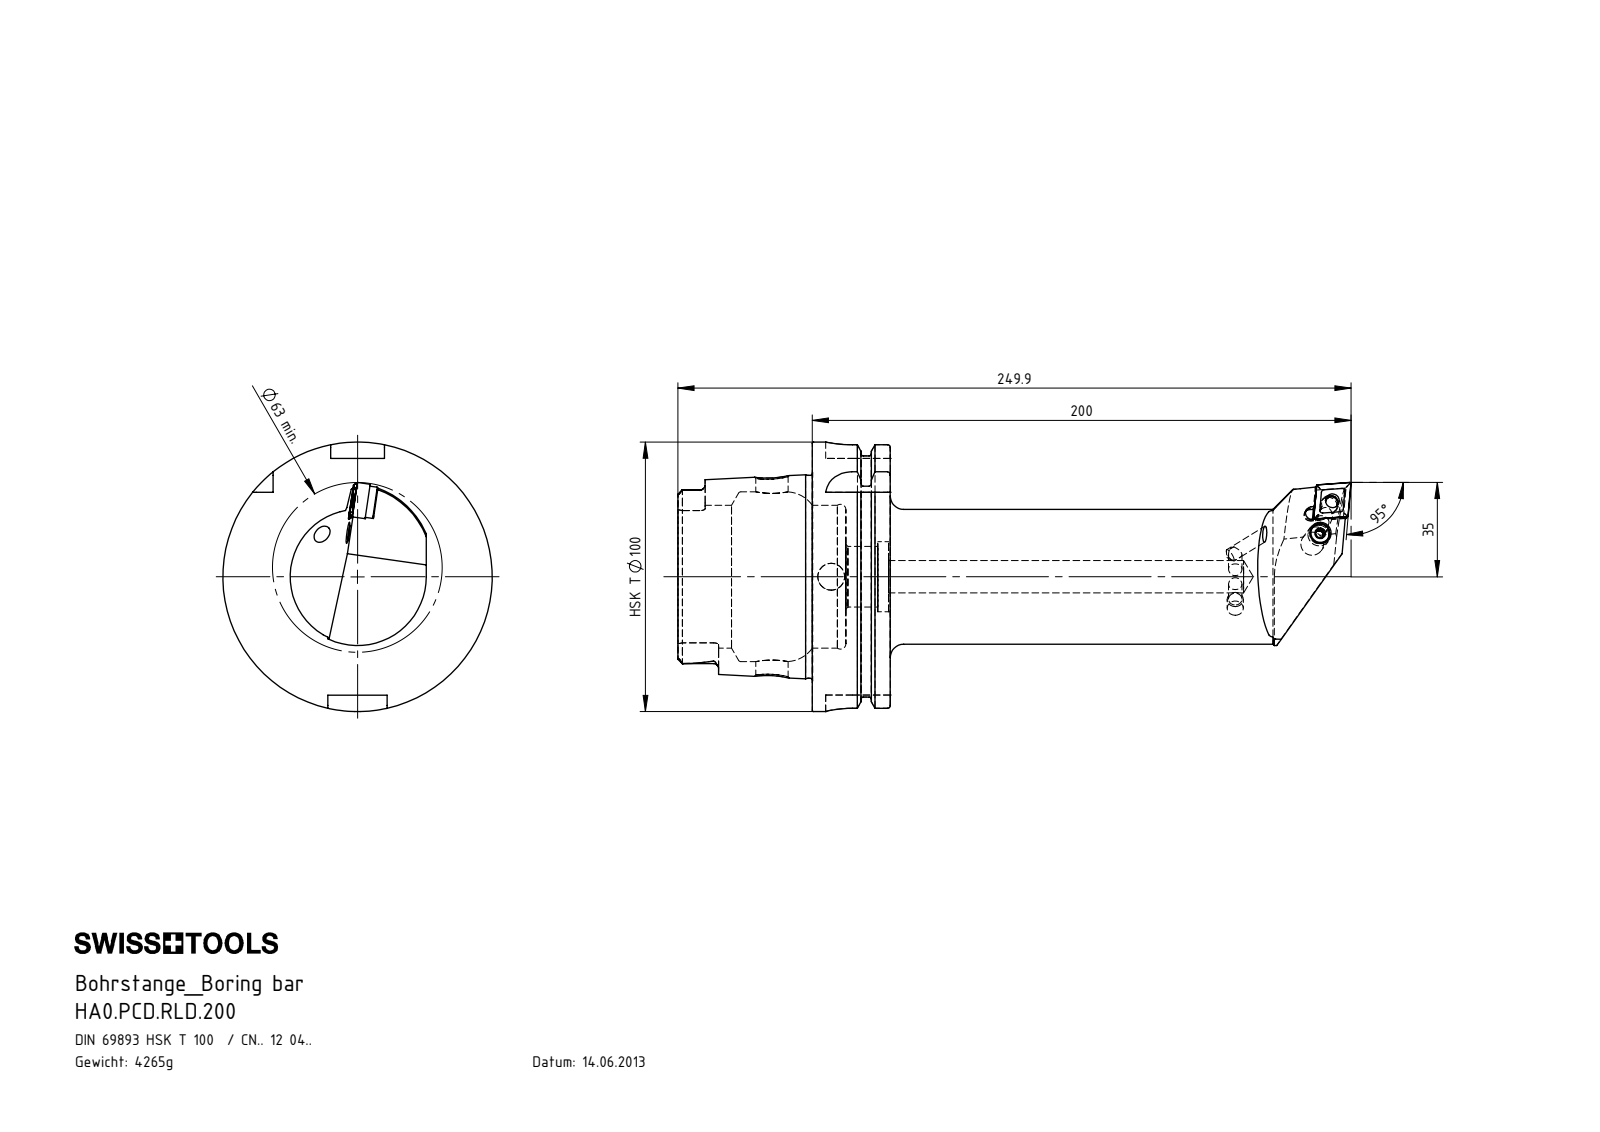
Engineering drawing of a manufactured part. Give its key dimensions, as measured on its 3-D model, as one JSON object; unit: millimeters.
{"part_name": "HA0-PCD.RLD.200; WCD-ER3.101.000_A; WCD-ER4.101.017_A; KVT_MB_600_060 (+3 more)", "step_written_by": "SolidWorks 2012 (CONFIG_CONTROL_DESIGN)", "units": "millimeters", "bodies": {"solids": 7, "faces": 366, "planar": 112, "cylindrical": 105, "other": 149}, "overall_size": [249.9, 100, 100], "volume_mm3": 540997, "surface_area_mm2": 83233, "round_holes": [[5, 3], [12, 2], [5.16, 1], [6, 1], [6.4, 1], [7, 1], [8.4, 1], [10, 1], [22.5, 1], [26, 1], [53, 1], [63, 1]], "round_bosses_or_shafts": [[100, 1], [91.95, 1], [75.26, 1], [50, 1], [8, 1], [7.9, 1], [6.4, 1], [6, 1]], "partial_cylinders_radius": [[1.9, 6], [0.4, 4], [1, 4], [10, 4], [2.5, 2], [4.83, 2], [4.88, 2], [2.1, 1]], "face_to_face_distances": [28.95, 12.45, 16.5, 49.9, 62.35, 78.85, 87.8, 78.2, 28.3, 15.85], "hole_center_spacings": [12.81, 12.86]}
